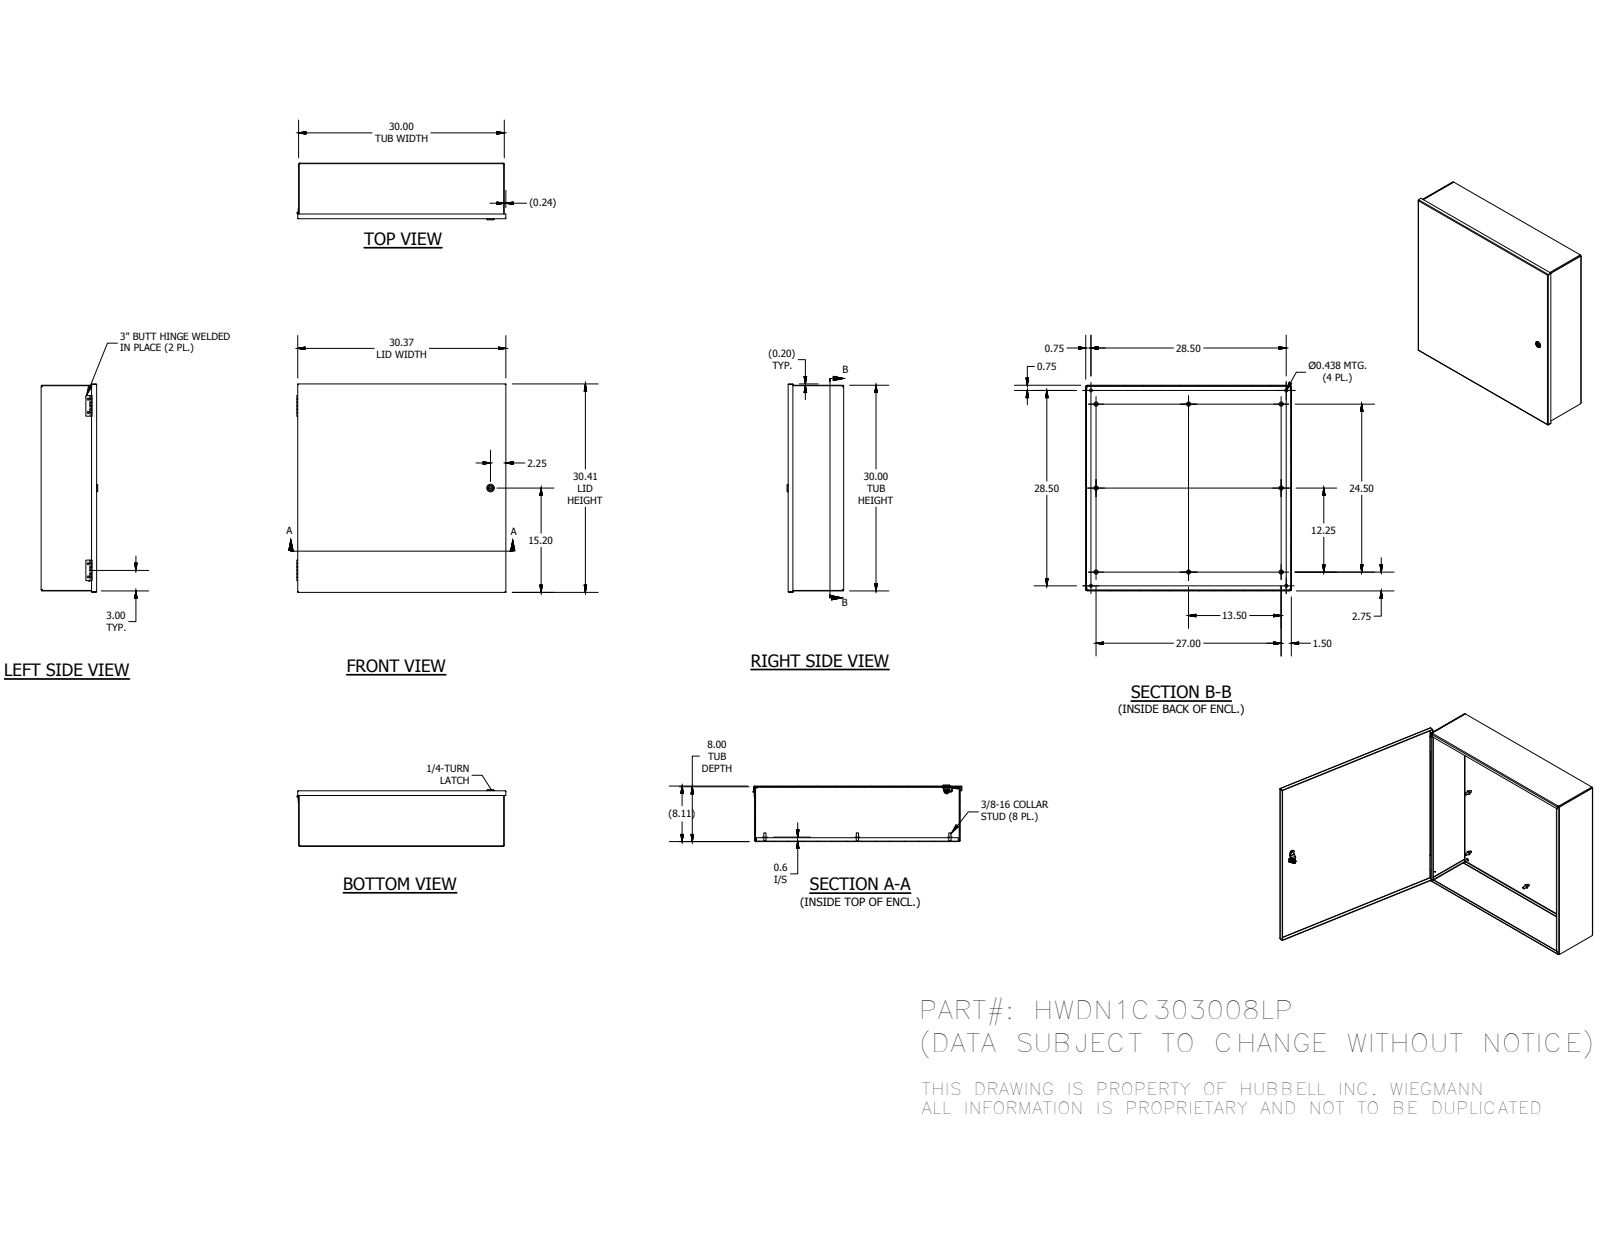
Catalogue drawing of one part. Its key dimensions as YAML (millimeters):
part_name: "N1C303008LPBLR; N1C3008LPTB; N1C3030LPLID; 1000-101-GPF_GPD (+8 more)"
step_written_by: "Autodesk Inventor 2016 (AUTOMOTIVE_DESIGN)"
units: millimeters
bodies: {solids: 25, faces: 749, planar: 453, cylindrical: 224, other: 72}
overall_size: [774.41, 772.32, 228.92]
volume: 3699000
surface_area: 3952000
round_holes:
  - {diameter: 7.95, count: 4}
  - {diameter: 11.11, count: 4}
  - {diameter: 3.05, count: 1}
  - {diameter: 3.3, count: 1}
  - {diameter: 5, count: 1}
  - {diameter: 8, count: 1}
  - {diameter: 10, count: 1}
  - {diameter: 10.2, count: 1}
  - {diameter: 16.1, count: 1}
  - {diameter: 20.38, count: 1}
round_bosses_or_shafts:
  - {diameter: 15.88, count: 8}
  - {diameter: 8.38, count: 8}
  - {diameter: 28, count: 1}
  - {diameter: 27, count: 1}
  - {diameter: 23, count: 1}
  - {diameter: 19.8, count: 1}
  - {diameter: 15.8, count: 1}
  - {diameter: 15.2, count: 1}
partial_cylinders:
  - {radius: 0.3, count: 30}
  - {radius: 1.59, count: 12}
  - {radius: 3.47, count: 12}
  - {radius: 0.5, count: 10}
  - {radius: 0.79, count: 4}
  - {radius: 2.67, count: 4}
  - {radius: 4, count: 4}
  - {radius: 0.4, count: 3}
face_to_face_distances: [1.88, 223.04, 760.12, 221.16, 224.92, 758.24, 762, 220.37, 2.67, 5.16]
hole_center_spacings: [723.9, 49.28, 363.37, 609.6, 780.82, 1023.75, 15.51, 64.39]
